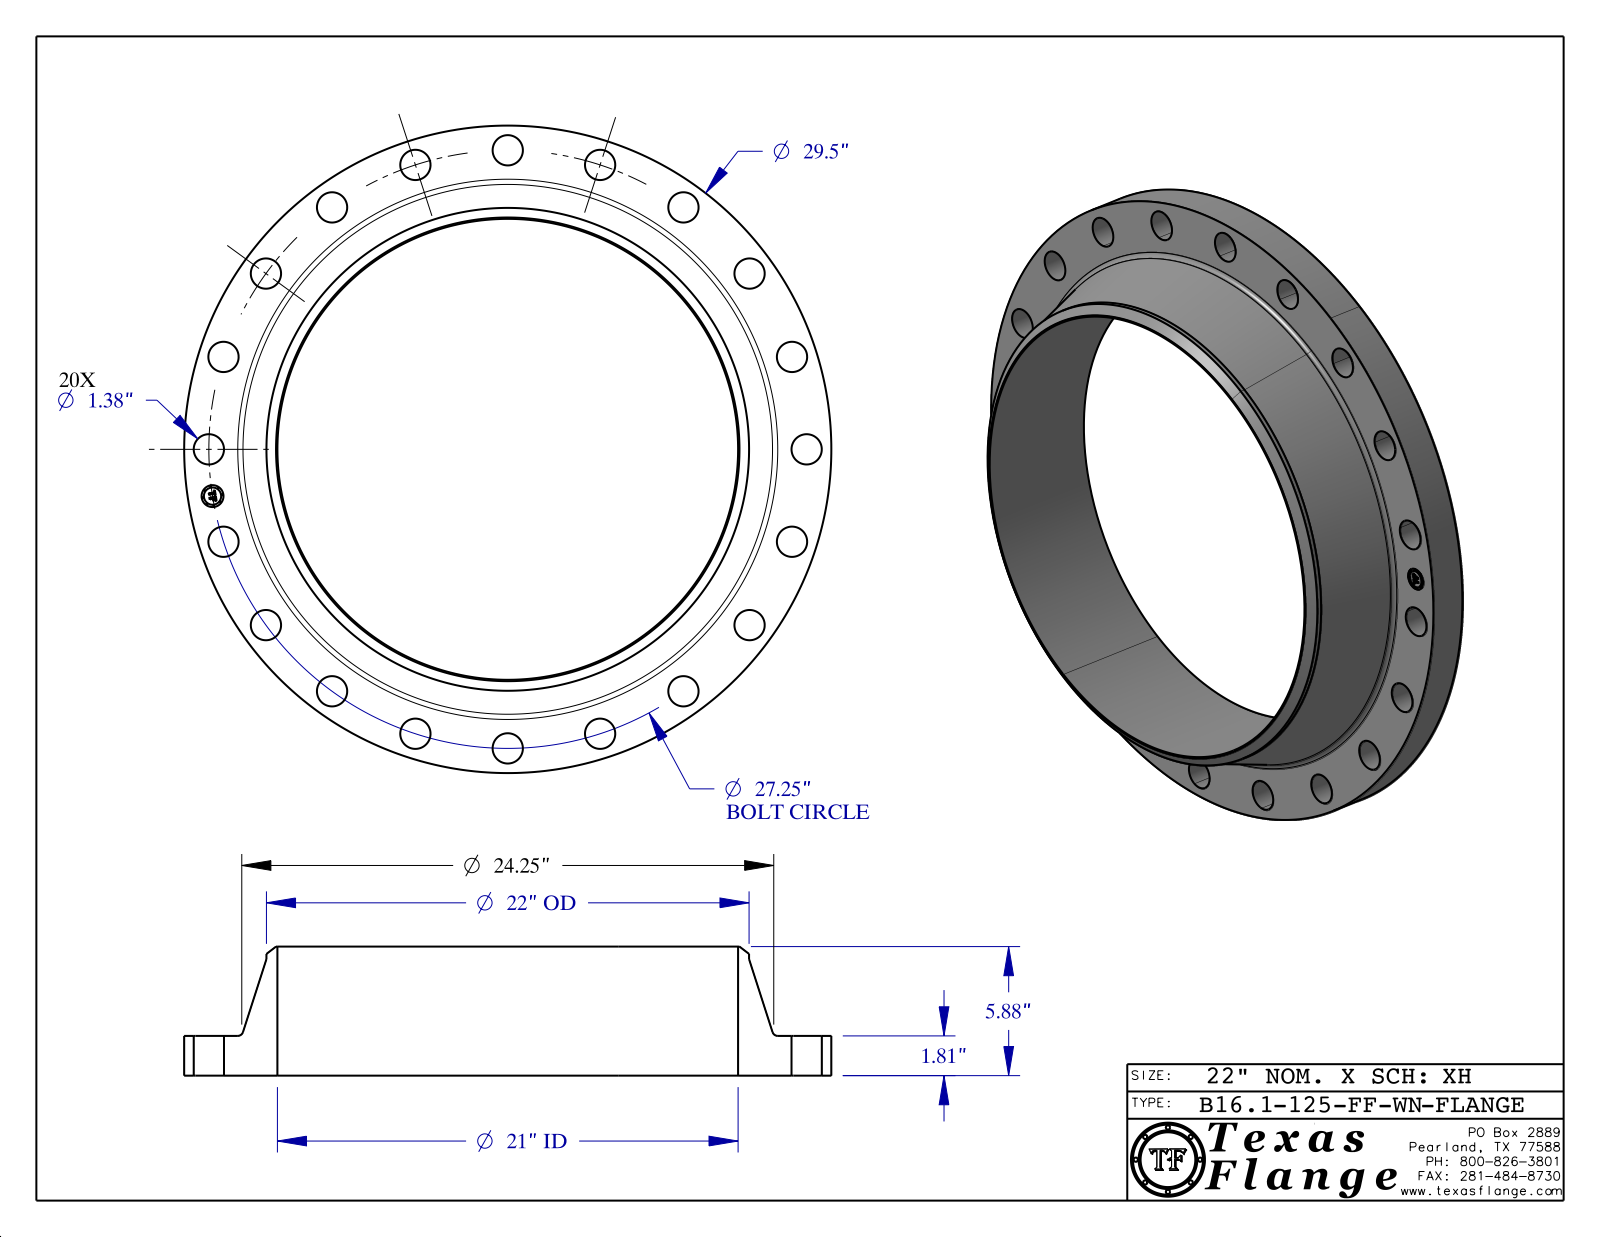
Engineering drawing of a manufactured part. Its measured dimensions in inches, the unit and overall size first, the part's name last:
Units: inches
Overall size (bounding box): 29.5 × 29.5 × 5.88
Round holes (diameter × count): ⌀1.38 ×20, ⌀1 ×1, ⌀21 ×1
Round bosses / shafts (diameter × count): ⌀0.061 ×8, ⌀29.5 ×1, ⌀22 ×1, ⌀0.788 ×1
Main face-to-face distances: 1.81, 5.88, 4.07, 1.795, 0.015, 4.085, 0.298, 0.293, 0.054, 0.193
Hole centre spacings: 13.625, 19.269, 25.917, 8.421, 12.371, 4.263, 16.017, 22.046
Volume: 829.6 in³ · Surface area: 1 533 in²
Bodies: 1 solid, 440 faces (368 planar, 66 cylindrical, 6 other)
Part name (STEP PRODUCT): B16.1, Class 125-FF-WN
STEP written by: CATIA V5 STEP AP214 (AUTOMOTIVE_DESIGN)
